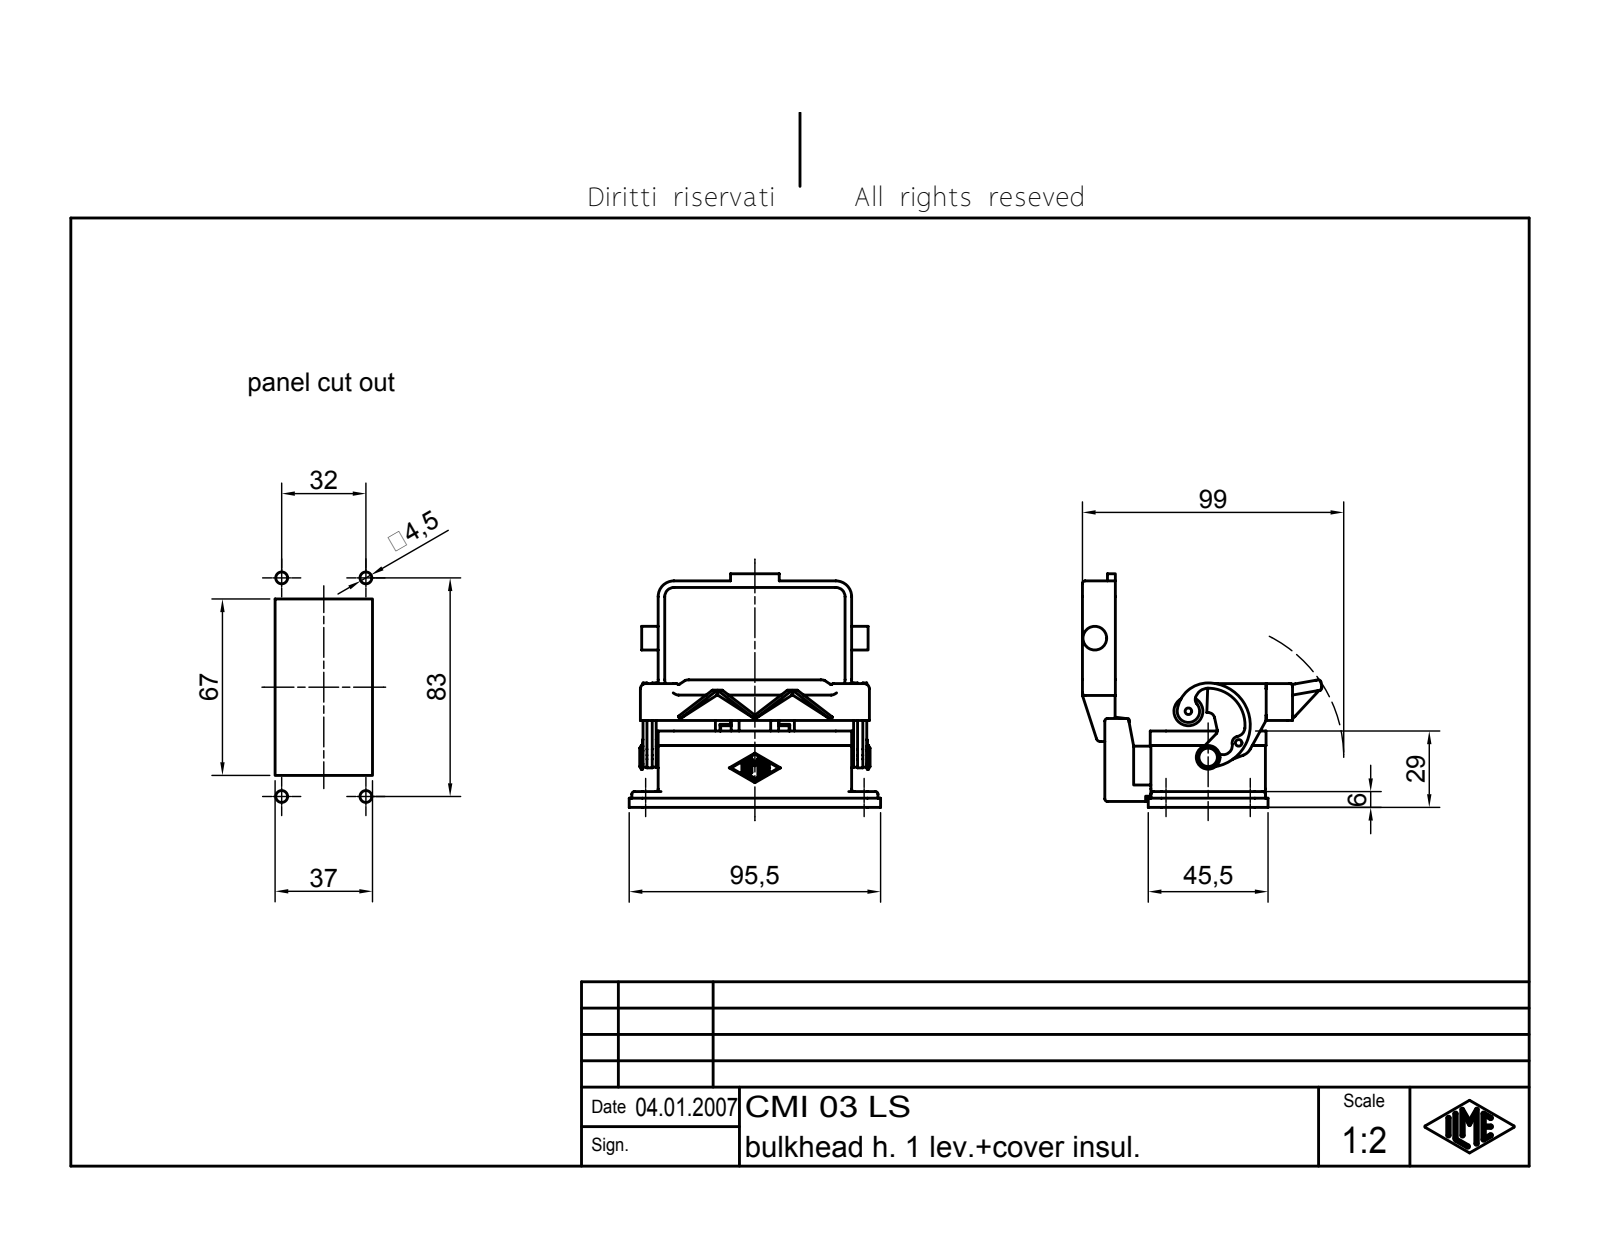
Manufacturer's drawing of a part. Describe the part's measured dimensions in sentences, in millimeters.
The part is named "CMI 03 LS". Its 3-D file was written by "Autodesk Inventor 7 (AUTOMOTIVE_DESIGN)". It is 6 solids with 628 faces: 240 planar, 209 cylindrical and 179 other. Overall it measures 95.5 by 90.95 by 88.7 millimeters. Its volume is 68 887 cubic millimeters and its surface area 46 251 square millimeters. Round holes: 4 of diameter 4.4, 4 of diameter 4.5, 1 of diameter 2, 1 of diameter 4. Round bosses or shafts: 2 of diameter 9, 2 of diameter 5, 1 of diameter 11, 1 of diameter 7, 1 of diameter 4, 1 of diameter 3, 1 of diameter 2.5. Partial cylindrical surfaces (rounded edges, fillets, slot ends): 24 of radius 1, 14 of radius 0.38, 12 of radius 2, 12 of radius 6, 7 of radius 2.5, 6 of radius 3.5, 6 of radius 5, 5 of radius 4. The main face-to-face distances are 4, 3, 3.5, 40.5, 2.5, 29, 25.5, 43.5, 0.75, 23.5. The hole center spacings are 32, 83, 88.96.
